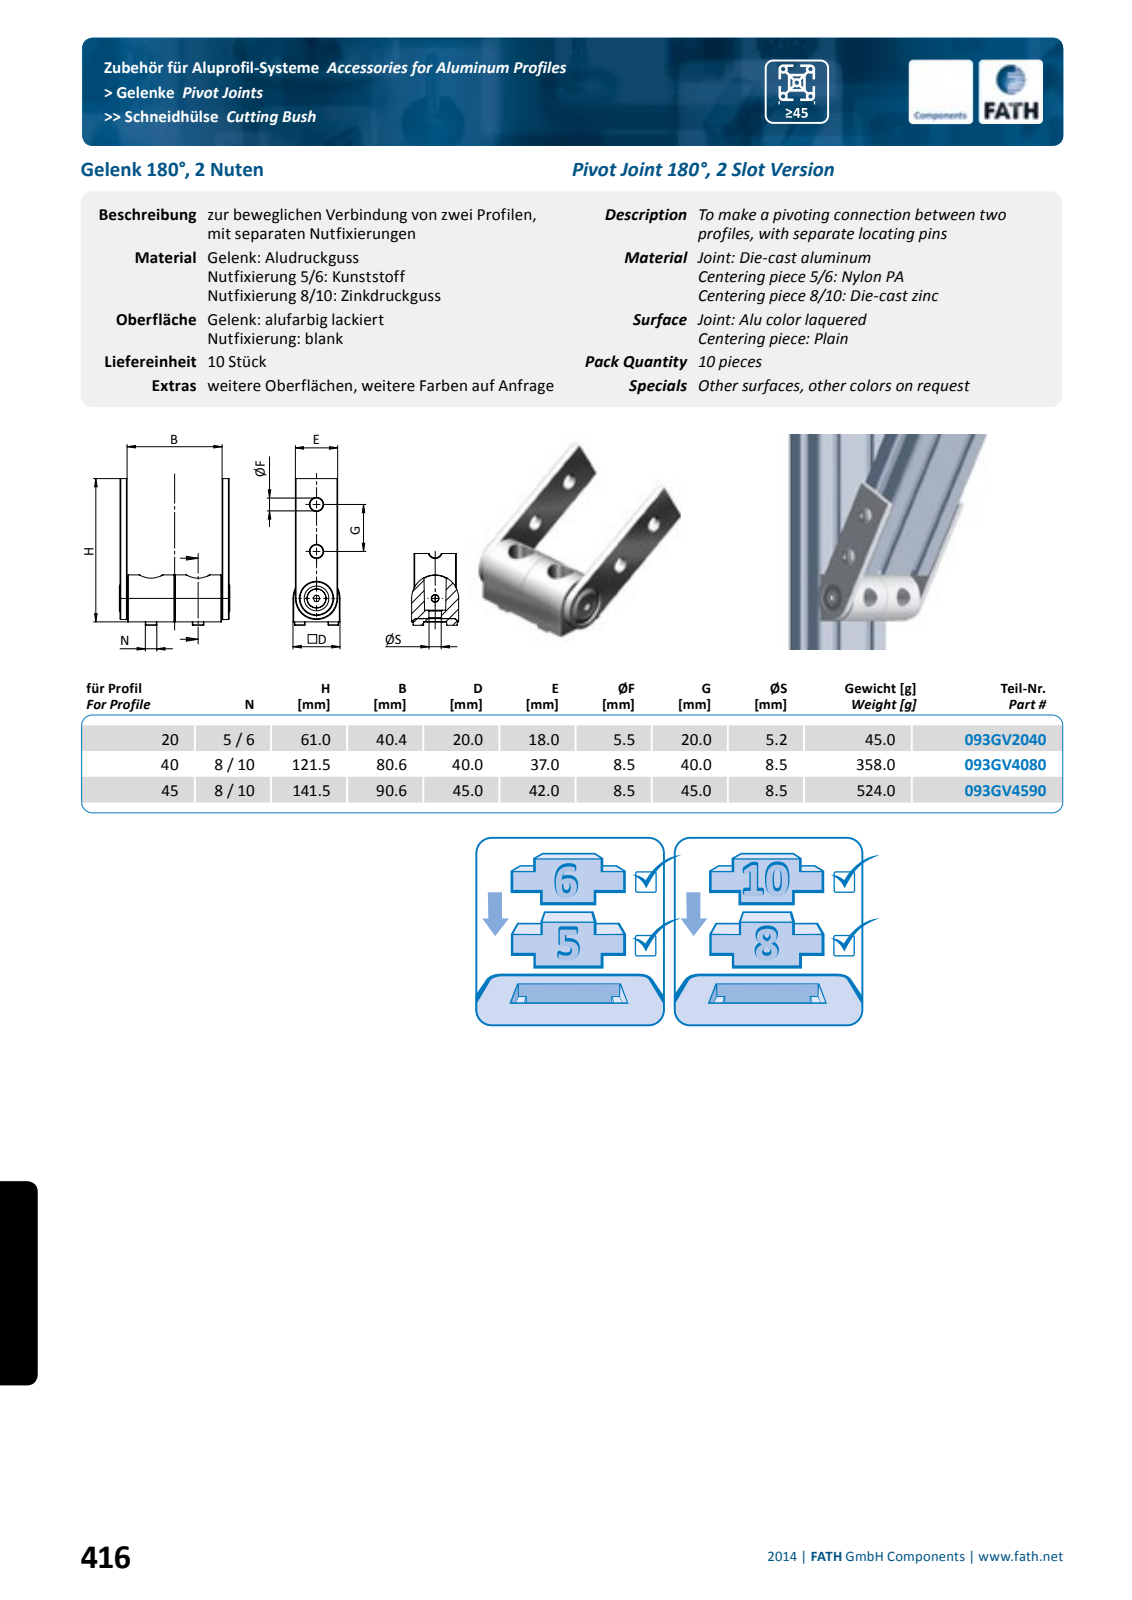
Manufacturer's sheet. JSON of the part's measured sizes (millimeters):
{"part_name": "093GV20R03_Standard; 093gv2040; 093GV20R02_Standard; 4din914m0410m_4 din 914 m04 10 (+5 more)", "step_written_by": "SolidWorks 2014 (AUTOMOTIVE_DESIGN)", "units": "millimeters", "bodies": {"solids": 13, "faces": 779, "planar": 269, "cylindrical": 208, "other": 302}, "overall_size": [62.45, 47, 20], "volume_mm3": 17038, "surface_area_mm2": 14137, "round_holes": [[1.5, 2], [5.2, 2], [5.5, 2], [3.3, 1], [6.2, 1], [8.2, 1], [11, 1], [14, 1], [17.1, 1]], "round_bosses_or_shafts": [[17, 1], [10.9, 1], [8, 1], [4, 1]], "partial_cylinders_radius": [[0.2, 44], [0.15, 12], [0.5, 8], [0.3, 4], [9, 1], [10, 1]], "face_to_face_distances": [43.4, 3, 40.4, 1, 23.2, 20.2, 20, 46.4, 19.2, 19], "hole_center_spacings": [7, 20, 21.19, 40.61, 14, 20.02, 40]}
